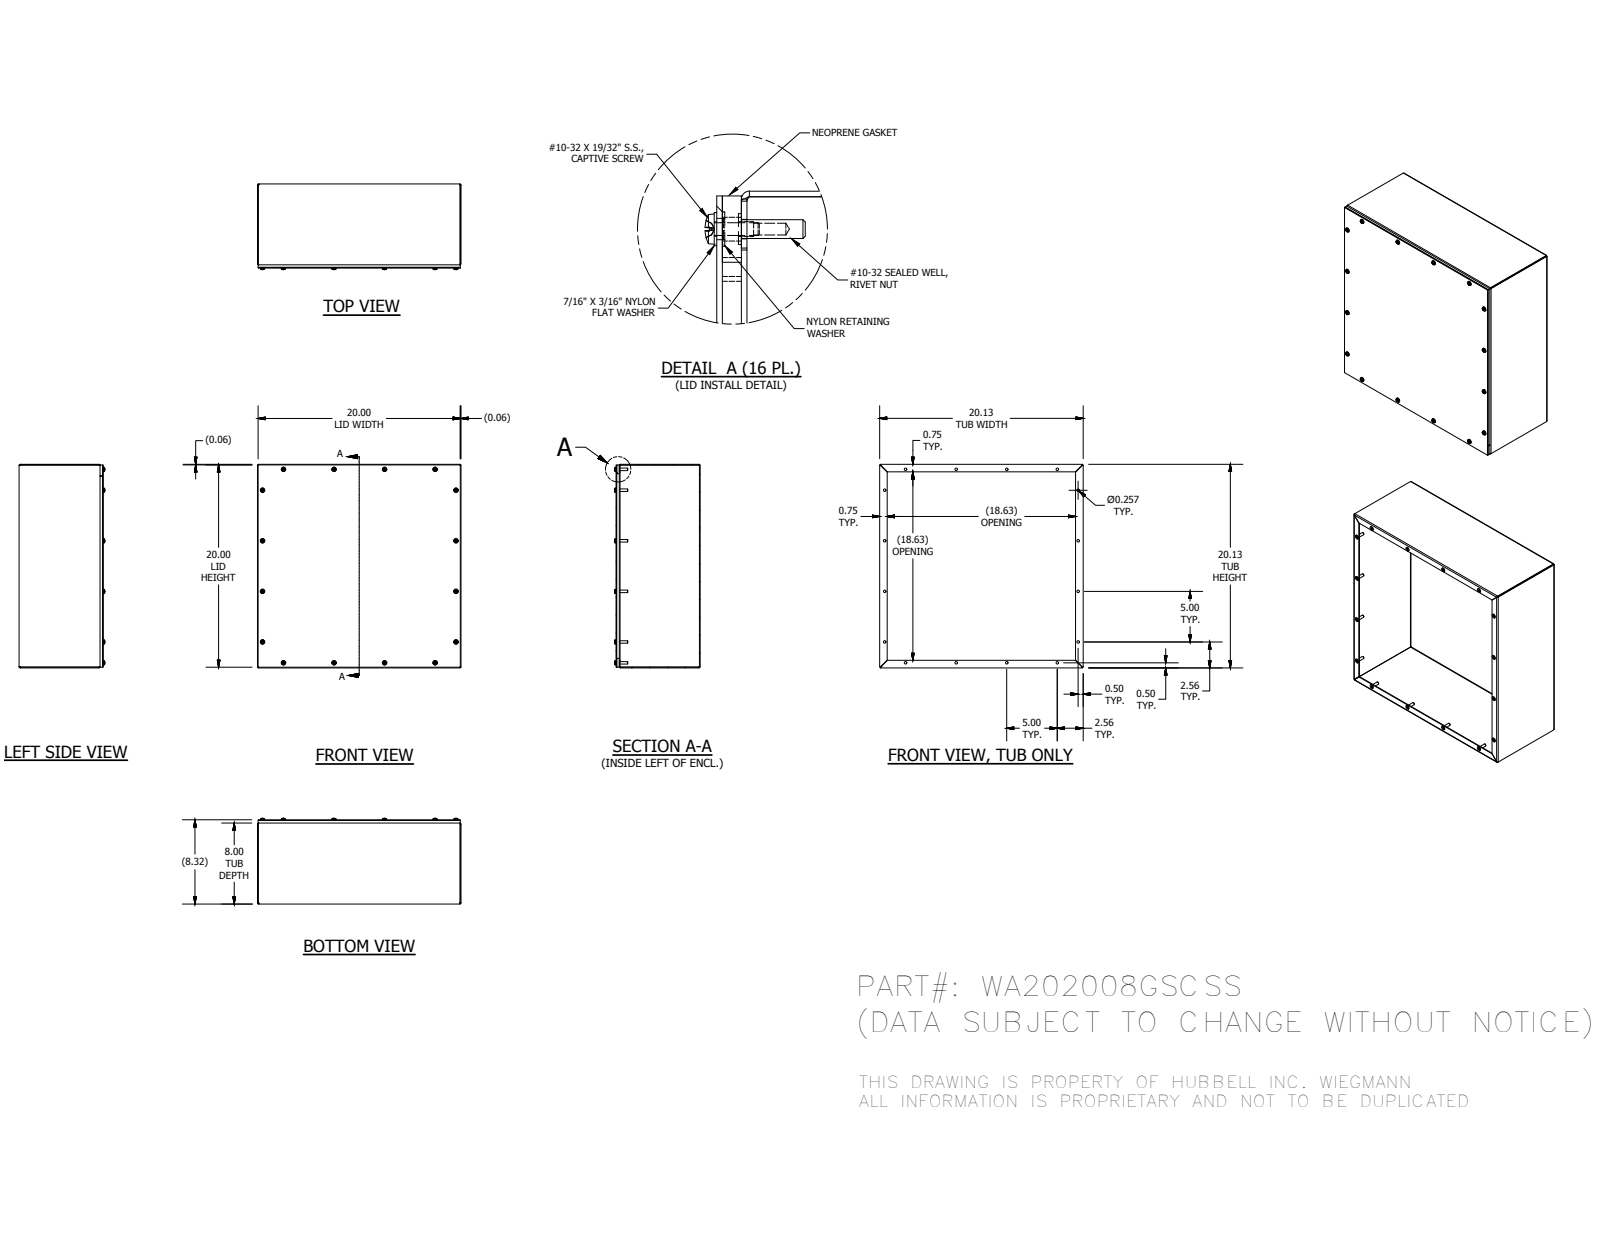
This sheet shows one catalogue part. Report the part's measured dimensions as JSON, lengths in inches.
{"part_name": "WA202008GSCSSBKP; WA2020GSCSSLID; 37210; 39035 (+4 more)", "step_written_by": "Autodesk Inventor 2016 (AUTOMOTIVE_DESIGN)", "units": "inches", "bodies": {"solids": 68, "faces": 1412, "planar": 772, "cylindrical": 288, "other": 352}, "overall_size": [20.125, 20.125, 8.478], "volume_in3": 127.2, "surface_area_in2": 3204, "round_holes": [[0.156, 16], [0.188, 16], [0.196, 16], [0.257, 16], [0.278, 16], [0.281, 16], [0.313, 16]], "round_bosses_or_shafts": [[0.453, 16], [0.437, 16], [0.406, 16], [0.248, 16], [0.167, 16]], "partial_cylinders_radius": [[0.089, 16], [0.031, 12], [0.07, 8], [0.105, 8]], "face_to_face_distances": [0.074, 8.25, 20.051, 8.324, 8.176, 19.977, 20.125, 7.926, 0.324, 0.25], "hole_center_spacings": [5, 10, 19.767, 7.357, 13.978, 19.124, 20.895, 21.581]}
